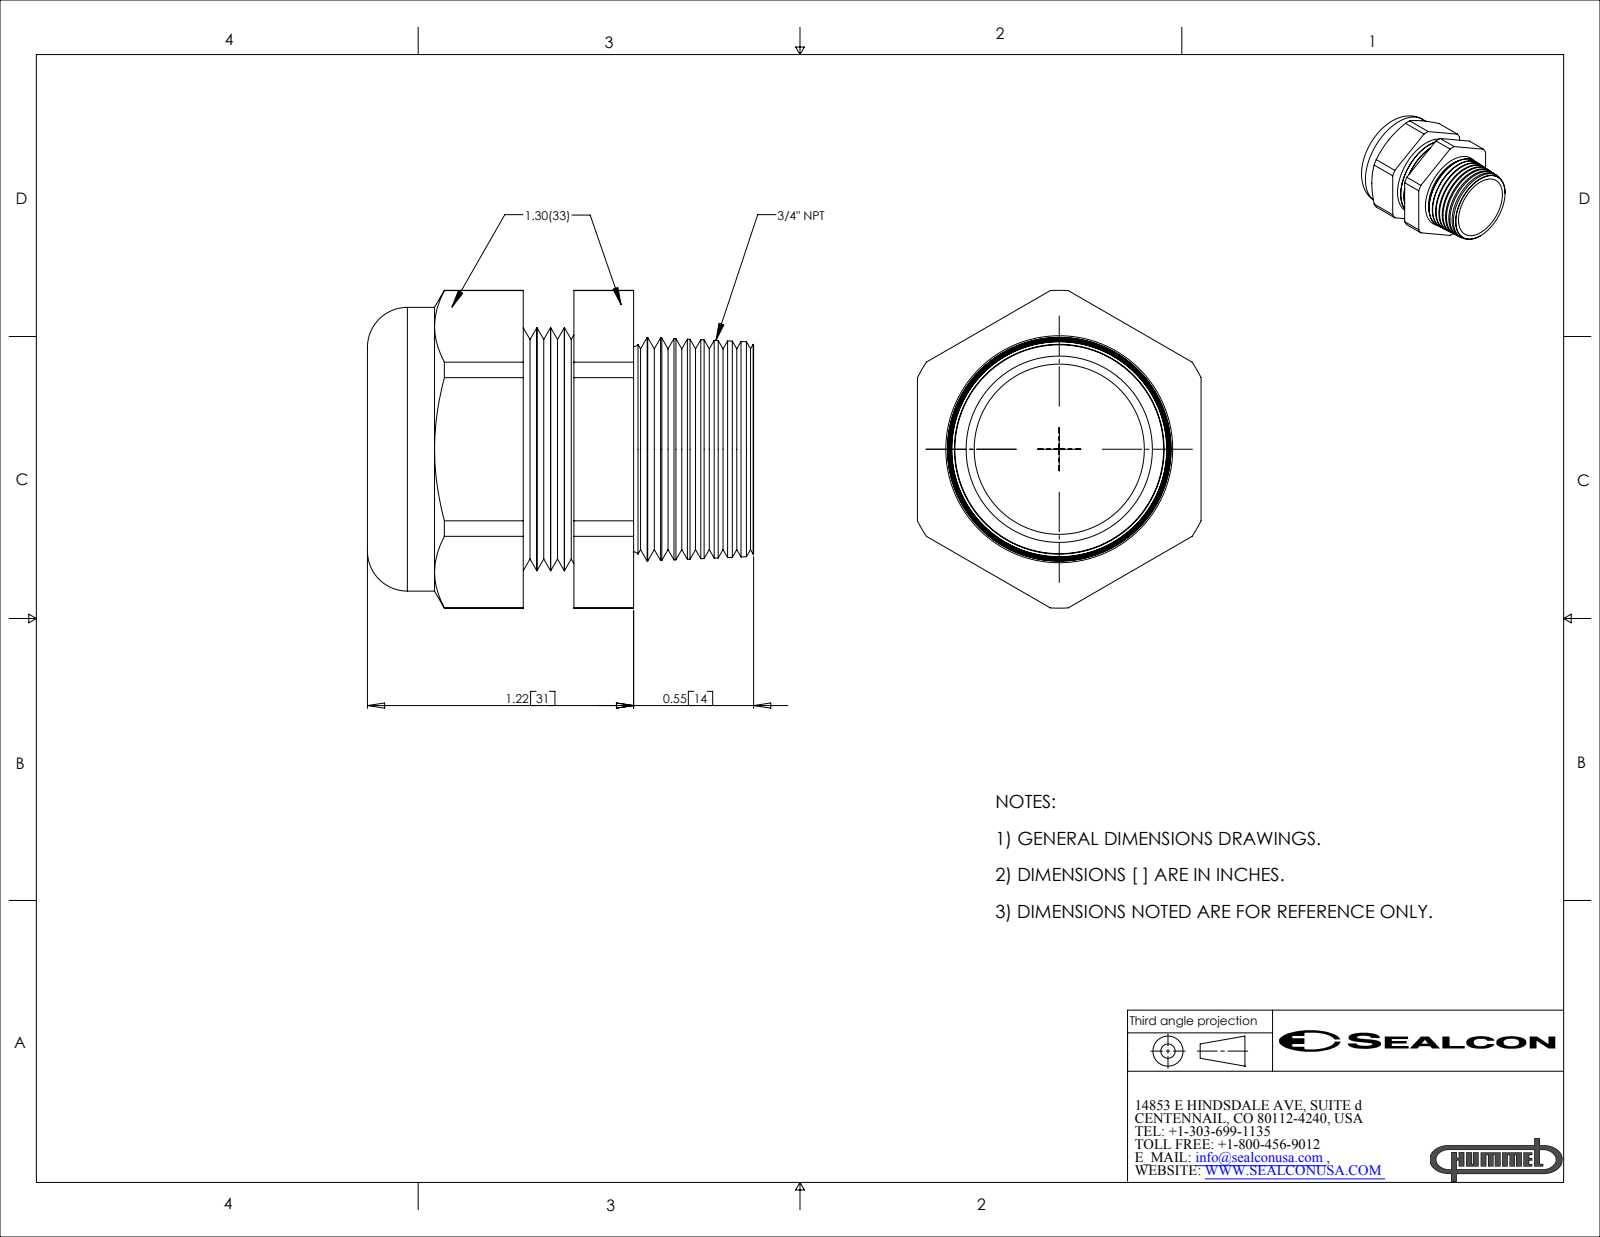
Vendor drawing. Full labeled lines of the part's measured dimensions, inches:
Part name (STEP PRODUCT): CD21NA-BK
STEP written by: SolidWorks 2007 (CONFIG_CONTROL_DESIGN)
Units: inches
Bodies: 2 solids, 136 faces (20 planar, 30 cylindrical, 86 other)
Overall size (bounding box): 1.77 × 1.456 × 1.3
Volume: 1.079 in³ · Surface area: 17.78 in²
Round holes (diameter × count): ⌀0.78 ×1, ⌀0.876 ×1
Round bosses / shafts (diameter × count): ⌀1.3 ×1, ⌀1.113 ×1
Partial cylindrical surfaces — rounded edges, fillets, slot ends (radius × count): R0.728 ×1
Main face-to-face distances: 1.3, 0.274, 0.232, 0.506, 0.407, 0.639, 0.913, 1.463, 1.056, 0.824
